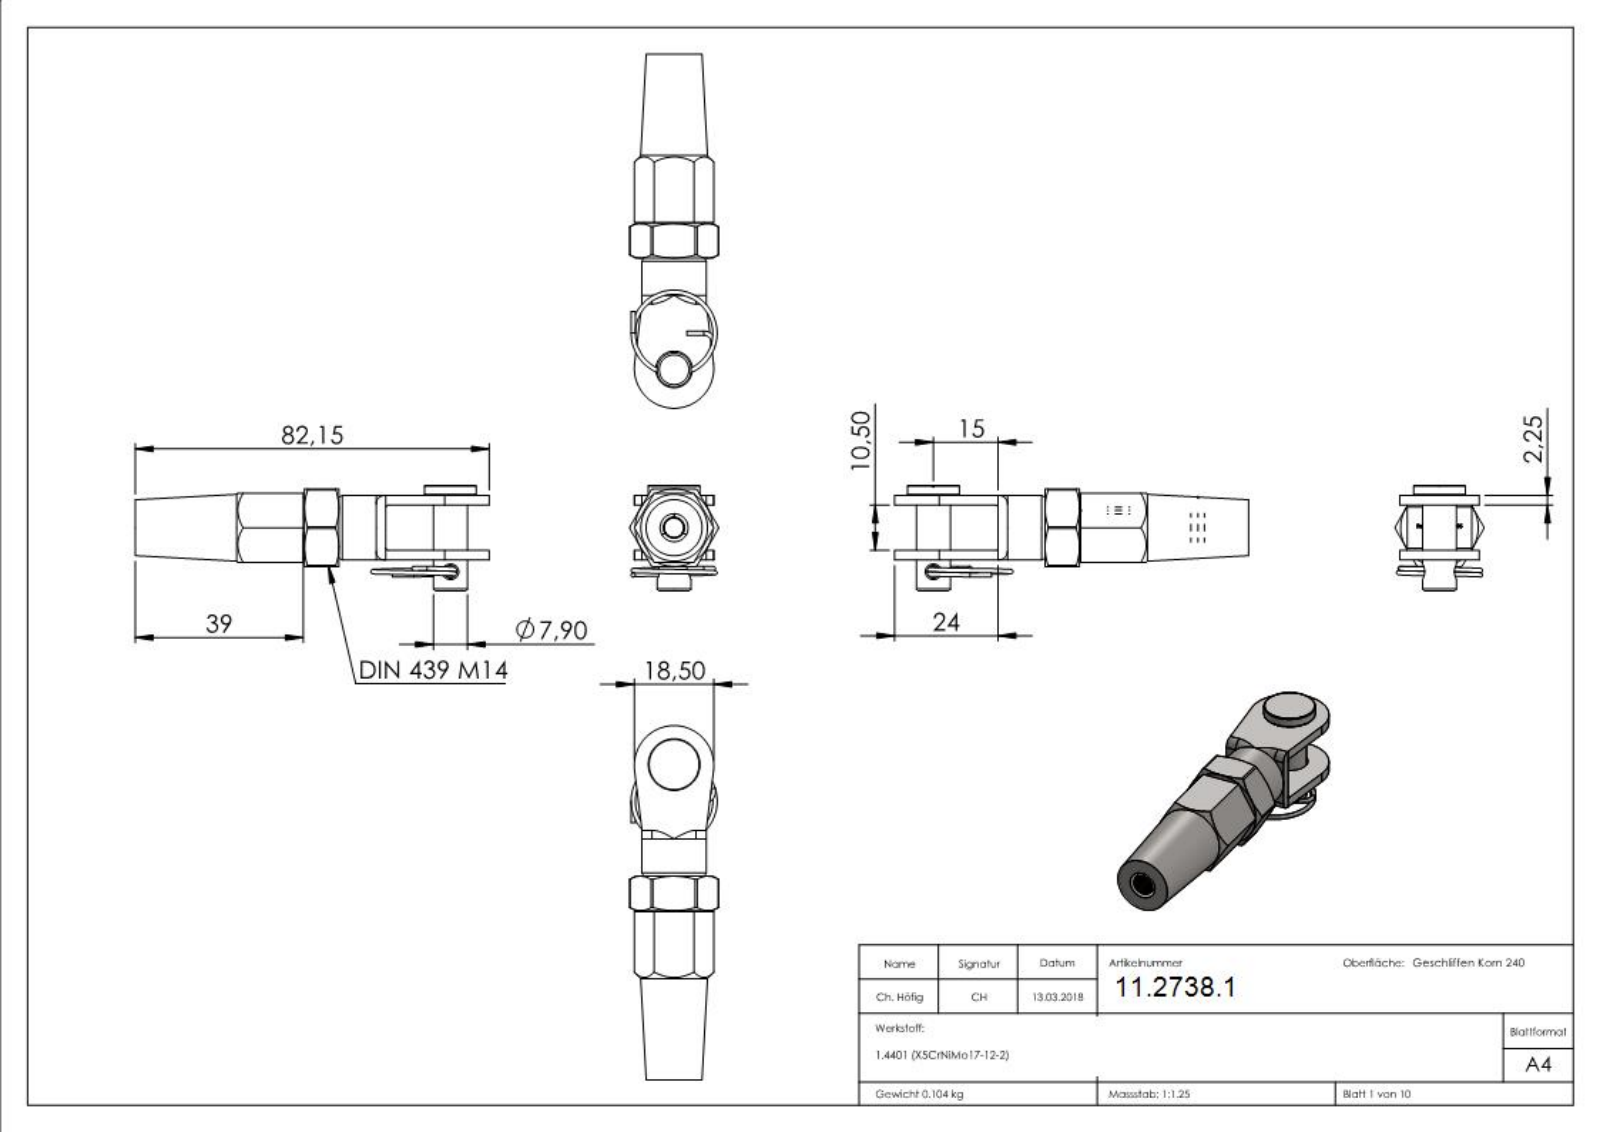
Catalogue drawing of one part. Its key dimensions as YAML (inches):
part_name: "10150005; 1015000X Teil4_10150005 Teil4; 1015000X Teil5_10150005 Teil5; 1015000X Teil7_10150005 Teil7 (+5 more)"
step_written_by: "SolidWorks 2015 (CONFIG_CONTROL_DESIGN)"
units: inches
bodies: {solids: 10, faces: 586, planar: 153, cylindrical: 153, other: 280}
overall_size: [3.234, 0.965, 0.812]
volume: 0.79
surface_area: 16.11
round_holes:
  - {diameter: 0.118, count: 1}
  - {diameter: 0.177, count: 1}
  - {diameter: 0.236, count: 1}
  - {diameter: 0.24, count: 1}
  - {diameter: 0.323, count: 1}
  - {diameter: 0.335, count: 1}
  - {diameter: 0.472, count: 1}
round_bosses_or_shafts:
  - {diameter: 0.039, count: 2}
  - {diameter: 0.591, count: 1}
  - {diameter: 0.551, count: 1}
  - {diameter: 0.472, count: 1}
  - {diameter: 0.394, count: 1}
  - {diameter: 0.311, count: 1}
partial_cylinders:
  - {radius: 0.02, count: 8}
  - {radius: 0.079, count: 2}
  - {radius: 0.364, count: 1}
face_to_face_distances: [0.089, 0.502, 0.039, 0.669, 0.63, 0.591, 0.413, 0.02, 0.108, 0.522]
